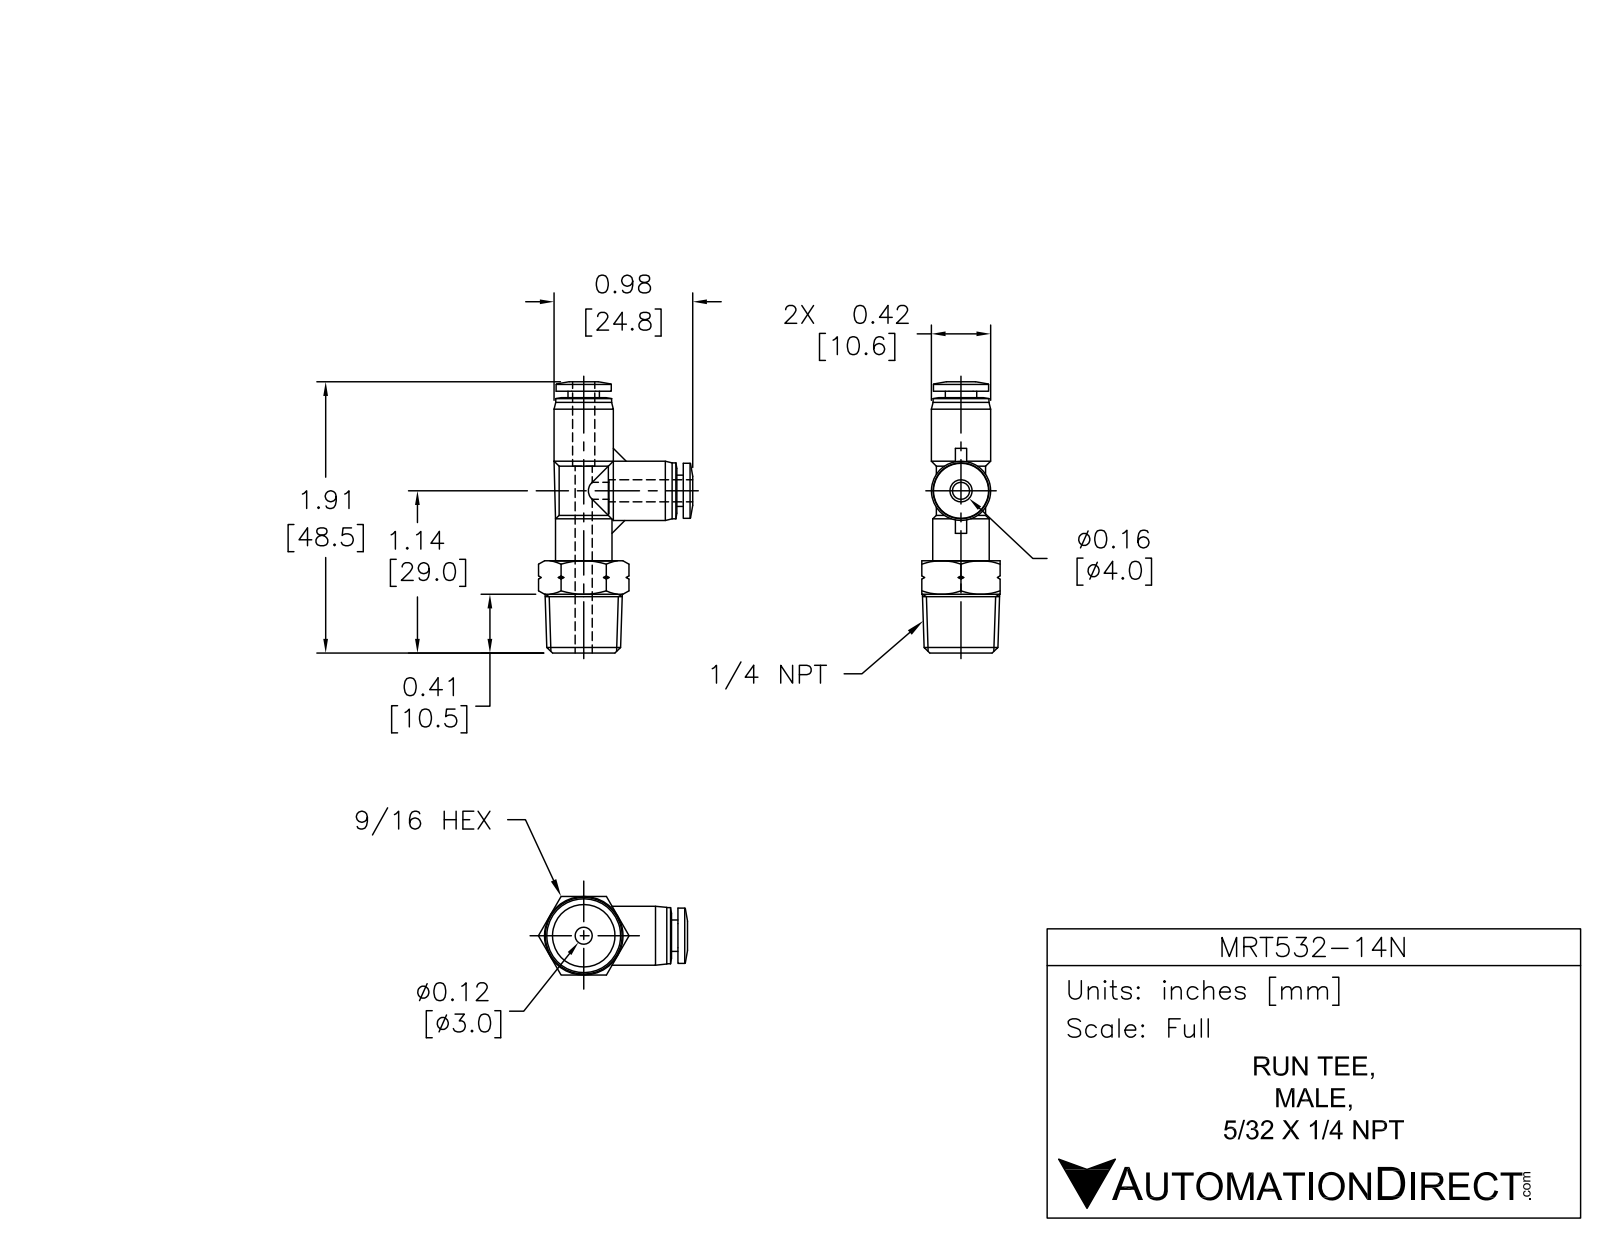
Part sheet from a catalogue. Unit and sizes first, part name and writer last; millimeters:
Units: millimetres
Overall size (bounding box): 48.5 × 27.6 × 14
Round holes (diameter × count): ⌀3 ×2, ⌀4.3 ×2
Round bosses / shafts (diameter × count): ⌀10.6 ×2, ⌀10 ×2, ⌀9.9 ×2, ⌀8.8 ×2, ⌀5.6 ×2, ⌀10.1 ×1
Main face-to-face distances: 14, 16.5, 46.8, 30.3, 1.1, 6, 8, 45.6, 29.2, 2
Volume: 5 440 mm³ · Surface area: 3 450 mm²
Bodies: 1 solid, 116 faces (23 planar, 30 cylindrical, 63 other)
Part name (STEP PRODUCT): MRT532-14N
STEP written by: SolidWorks 2015 (AUTOMOTIVE_DESIGN)
